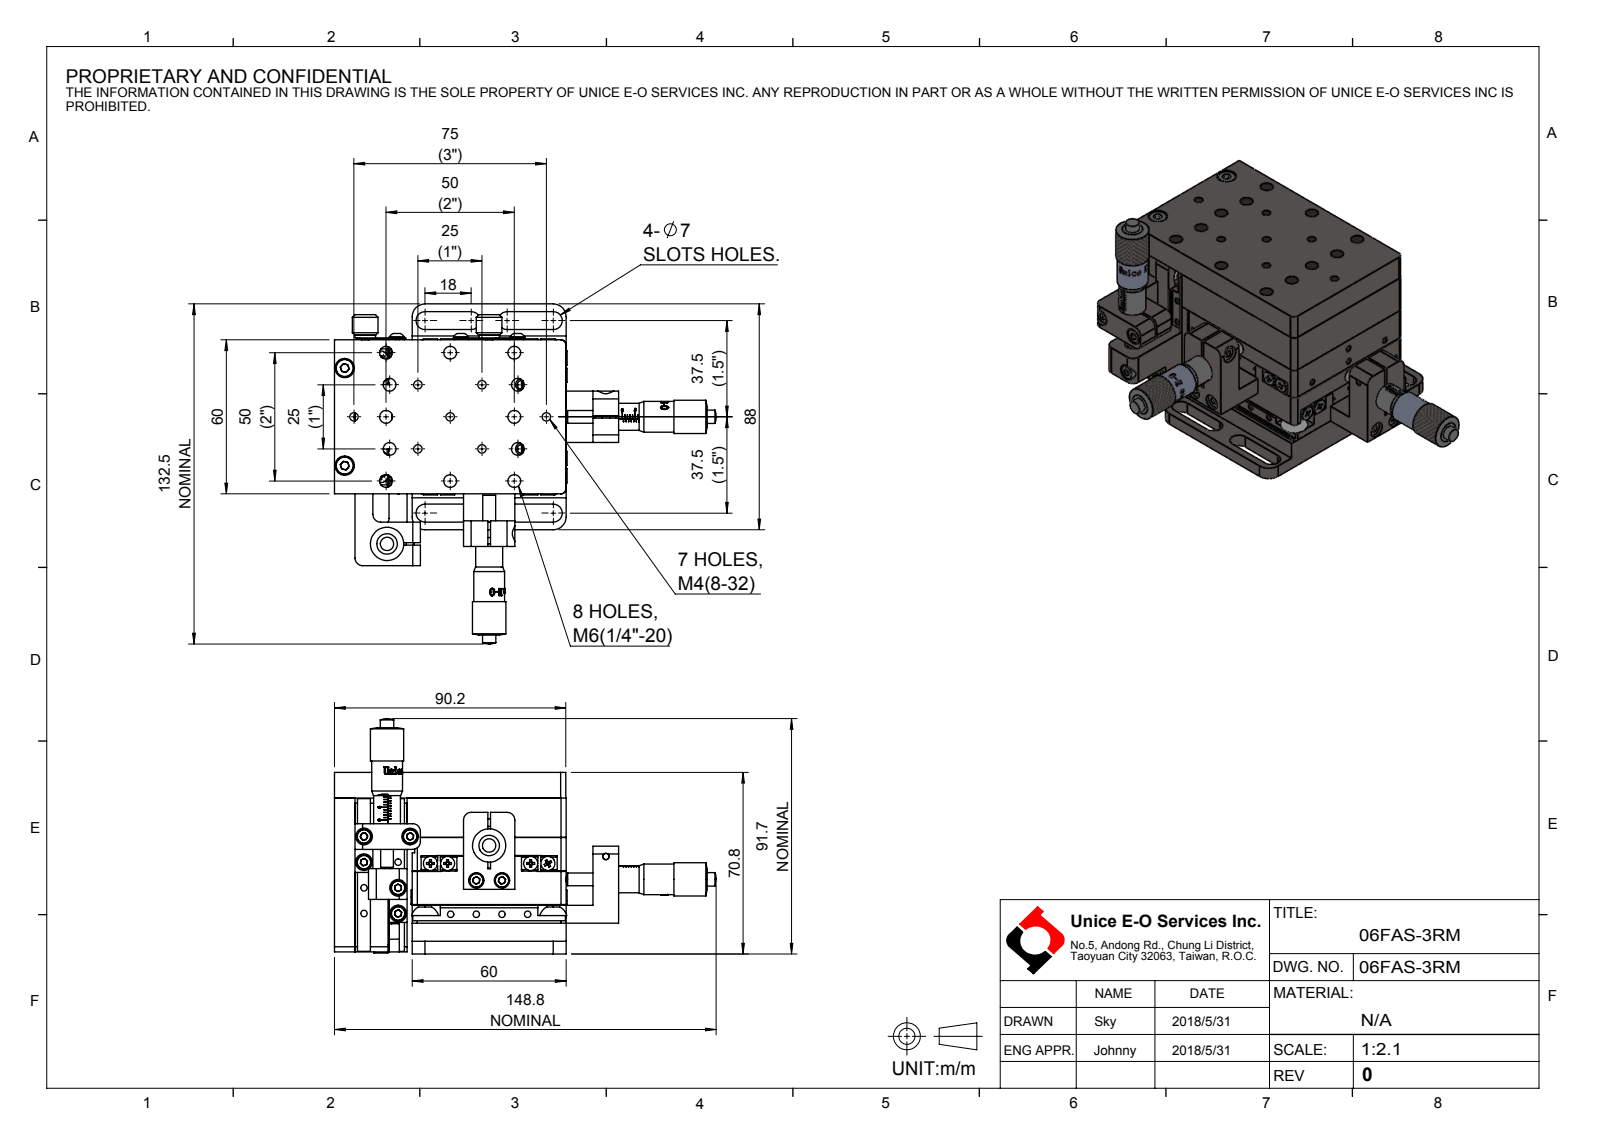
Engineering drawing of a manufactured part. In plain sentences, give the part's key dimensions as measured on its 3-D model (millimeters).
The part is named "06FAS-3RM". Its 3-D file was written by "SolidWorks 2016 (AUTOMOTIVE_DESIGN)". It is 0 solids with 1397 faces: 813 planar, 373 cylindrical and 211 other. Overall it measures 148.8 by 132.5 by 91.7 millimeters. Round holes: 18 of diameter 2.5, 18 of diameter 5, 9 of diameter 6.5, 8 of diameter 2.05, 7 of diameter 3.3, 6 of diameter 6, 4 of diameter 8, 2 of diameter 3.1, 2 of diameter 7.5, 1 of diameter 9.5. Round bosses or shafts: 18 of diameter 5.5, 5 of diameter 7, 4 of diameter 5.7, 3 of diameter 13, 3 of diameter 12, 3 of diameter 10.5, 3 of diameter 6, 3 of diameter 5.2. Partial cylindrical surfaces (rounded edges, fillets, slot ends): 11 of radius 3, 10 of radius 2, 8 of radius 3.5, 4 of radius 1.75, 4 of radius 5, 3 of radius 5.98. The main face-to-face distances are 7, 13.3, 20.3, 13.1, 60, 13.2, 10, 60.8, 6.1, 6. The hole center spacings are 25, 10, 35.36, 55.9, 50, 12.58, 17.61, 17.75.
